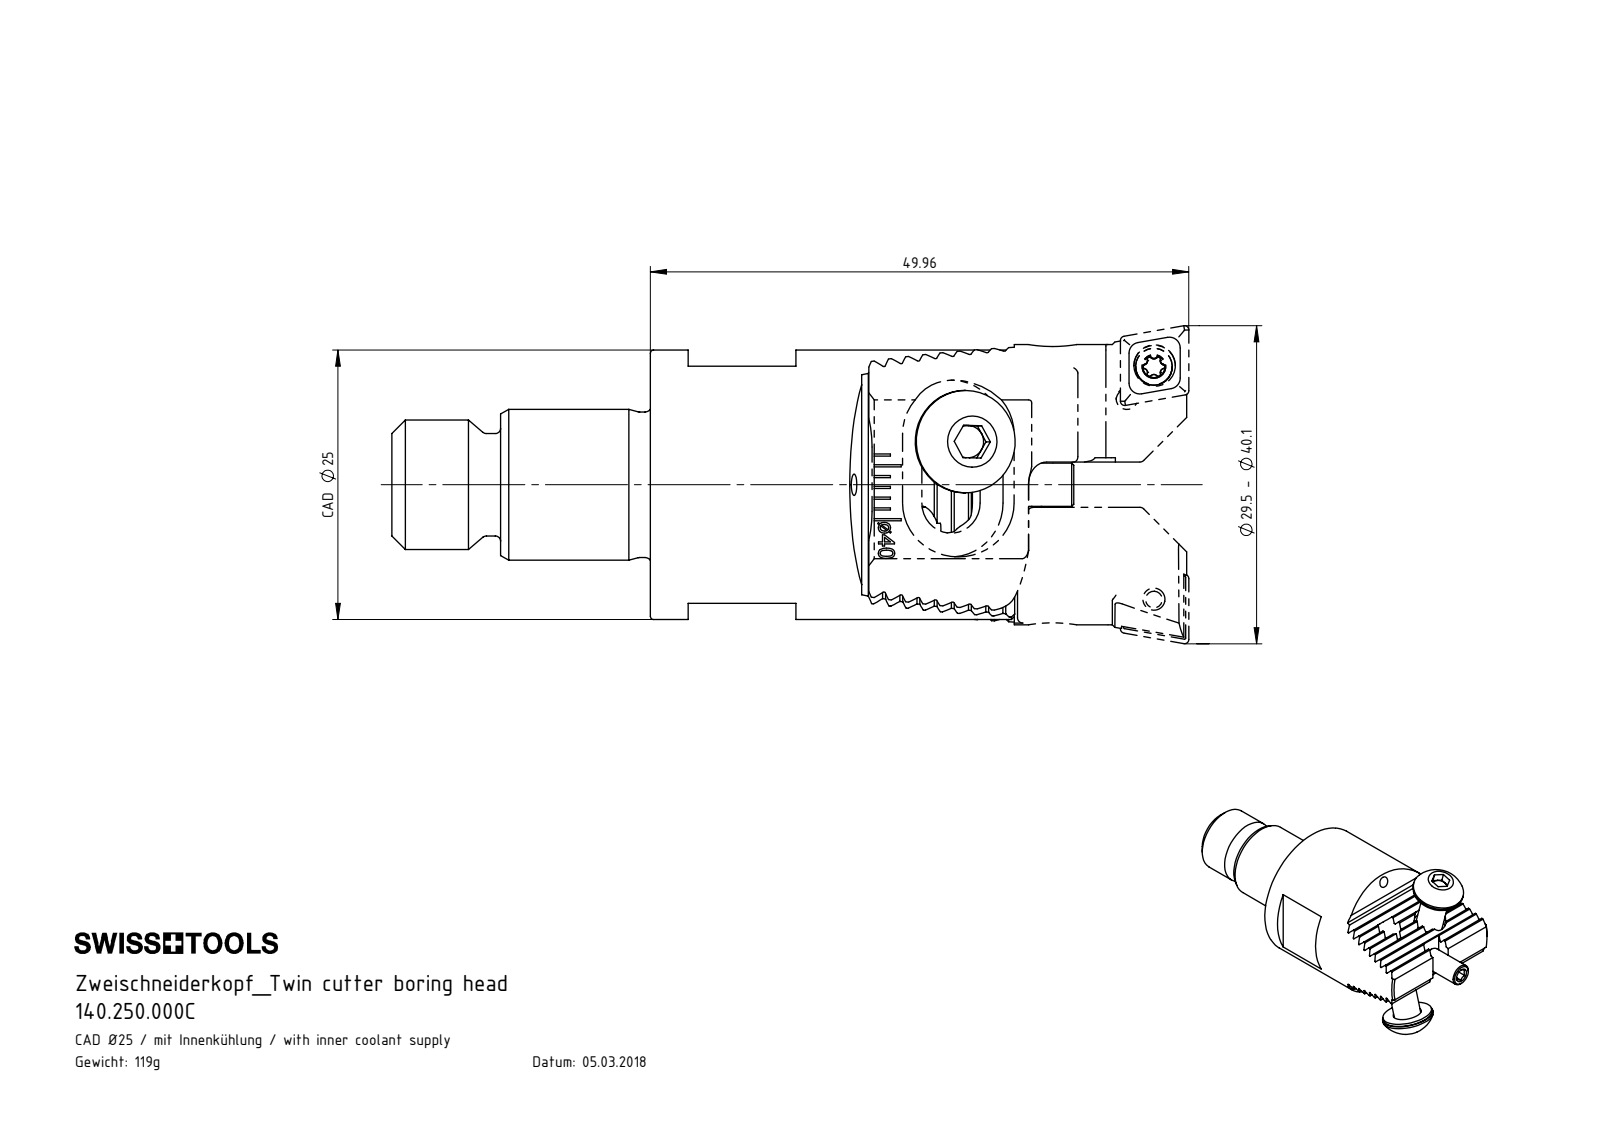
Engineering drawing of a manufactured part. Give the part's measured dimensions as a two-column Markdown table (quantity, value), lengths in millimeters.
| quantity | value |
| --- | --- |
| part name | WCA-ER2.001.006_A; CA2-Z25.K23.050_A; 140.250.000C; Z25-ER1.001.012 (+8 more) |
| STEP written by | SolidWorks 2017 (CONFIG_CONTROL_DESIGN) |
| units | millimeters |
| bodies | 15 solids, 1010 faces (481 planar, 253 cylindrical, 276 other) |
| overall size | 73.96 × 29.5 × 25 |
| volume | 21 088 mm³ |
| surface area | 11 568 mm² |
| round holes (diameter × count) | 2 × 6, 1.6 × 2, 2.05 × 2, 2.8 × 2, 3.85 × 2, 4.2 × 2, 5.3 × 2, 6 × 2, 2.5 × 1, 3.3 × 1, 3.5 × 1 |
| round bosses / shafts (diameter × count) | 9.5 × 3, 9.2 × 2, 5 × 2, 4 × 2, 3.4 × 2, 2.5 × 2, 25 × 1, 14 × 1 |
| partial cylindrical surfaces (radius × count) | 0.12 × 18, 0.5 × 18, 0.12 × 16, 0.21 × 12, 0.36 × 10, 2 × 4, 2.8 × 4, 5 × 4 |
| main face-to-face distances | 1.43, 2.86, 4.29, 5.72, 7.14, 5.71, 7.15, 8.57, 1.36, 4.28 |
| hole center spacings | 3.91, 4.01, 7, 19.06, 19.15, 21.97, 13.52, 15.9 |
